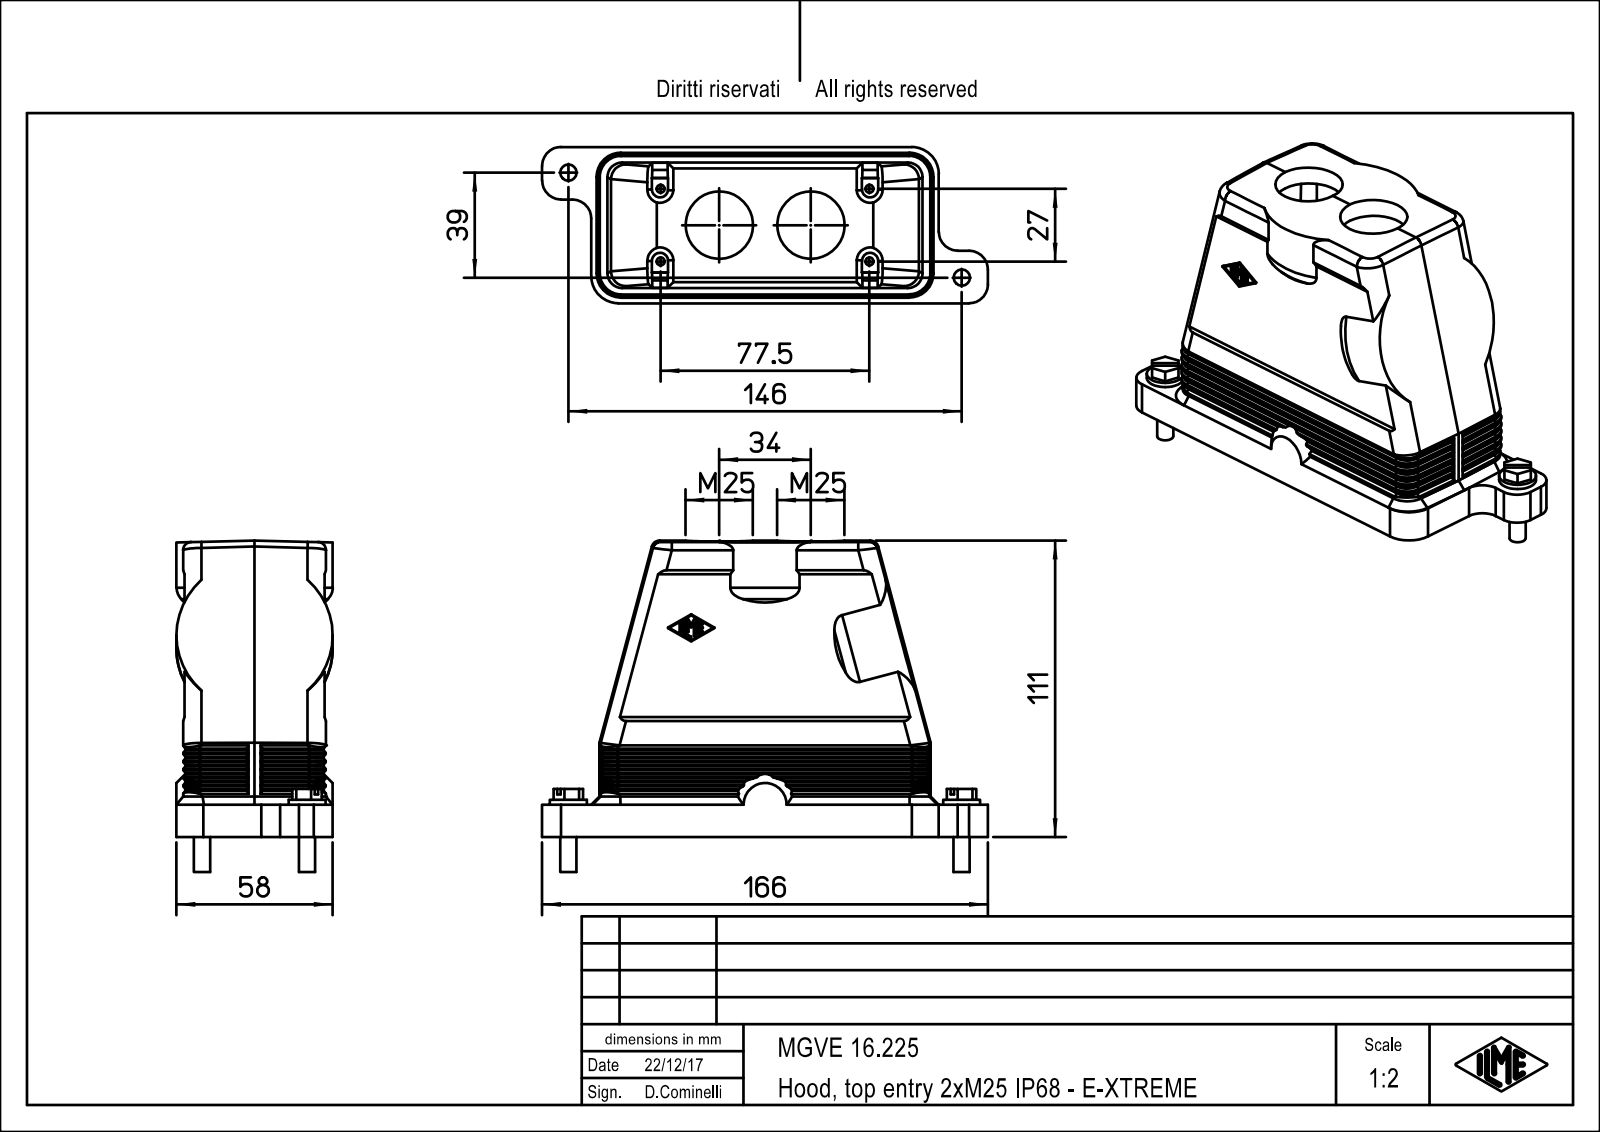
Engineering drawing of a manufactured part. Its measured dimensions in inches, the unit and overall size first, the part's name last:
Units: inches
Overall size (bounding box): 6.516 × 4.843 × 2.283
Round holes (diameter × count): ⌀0.118 ×4, ⌀0.984 ×2
Round bosses / shafts (diameter × count): ⌀0.539 ×2, ⌀0.236 ×2
Partial cylindrical surfaces — rounded edges, fillets, slot ends (radius × count): R0.276 ×62, R0.013 ×15, R0.217 ×8, R0.335 ×4, R0.007 ×2, R0.394 ×2, R1.142 ×2, R0.007 ×1
Main face-to-face distances: 2.047, 0.118, 2.165, 0.098, 0.02, 2.185, 2.067, 3.071, 0.131, 2.283
Hole centre spacings: 1.008, 2.258, 1.063, 3.051, 3.231, 1.339
Volume: 11.27 in³ · Surface area: 131.6 in²
Bodies: 1 solid, 535 faces (254 planar, 125 cylindrical, 156 other)
Part name (STEP PRODUCT): MGVE_16.225
STEP written by: PTC Creo Elements/Direct Modeling 19.0E 27-Jun-2016 (C) Parametric Technology GmbH (AUTOMOTIVE_DESIGN)
